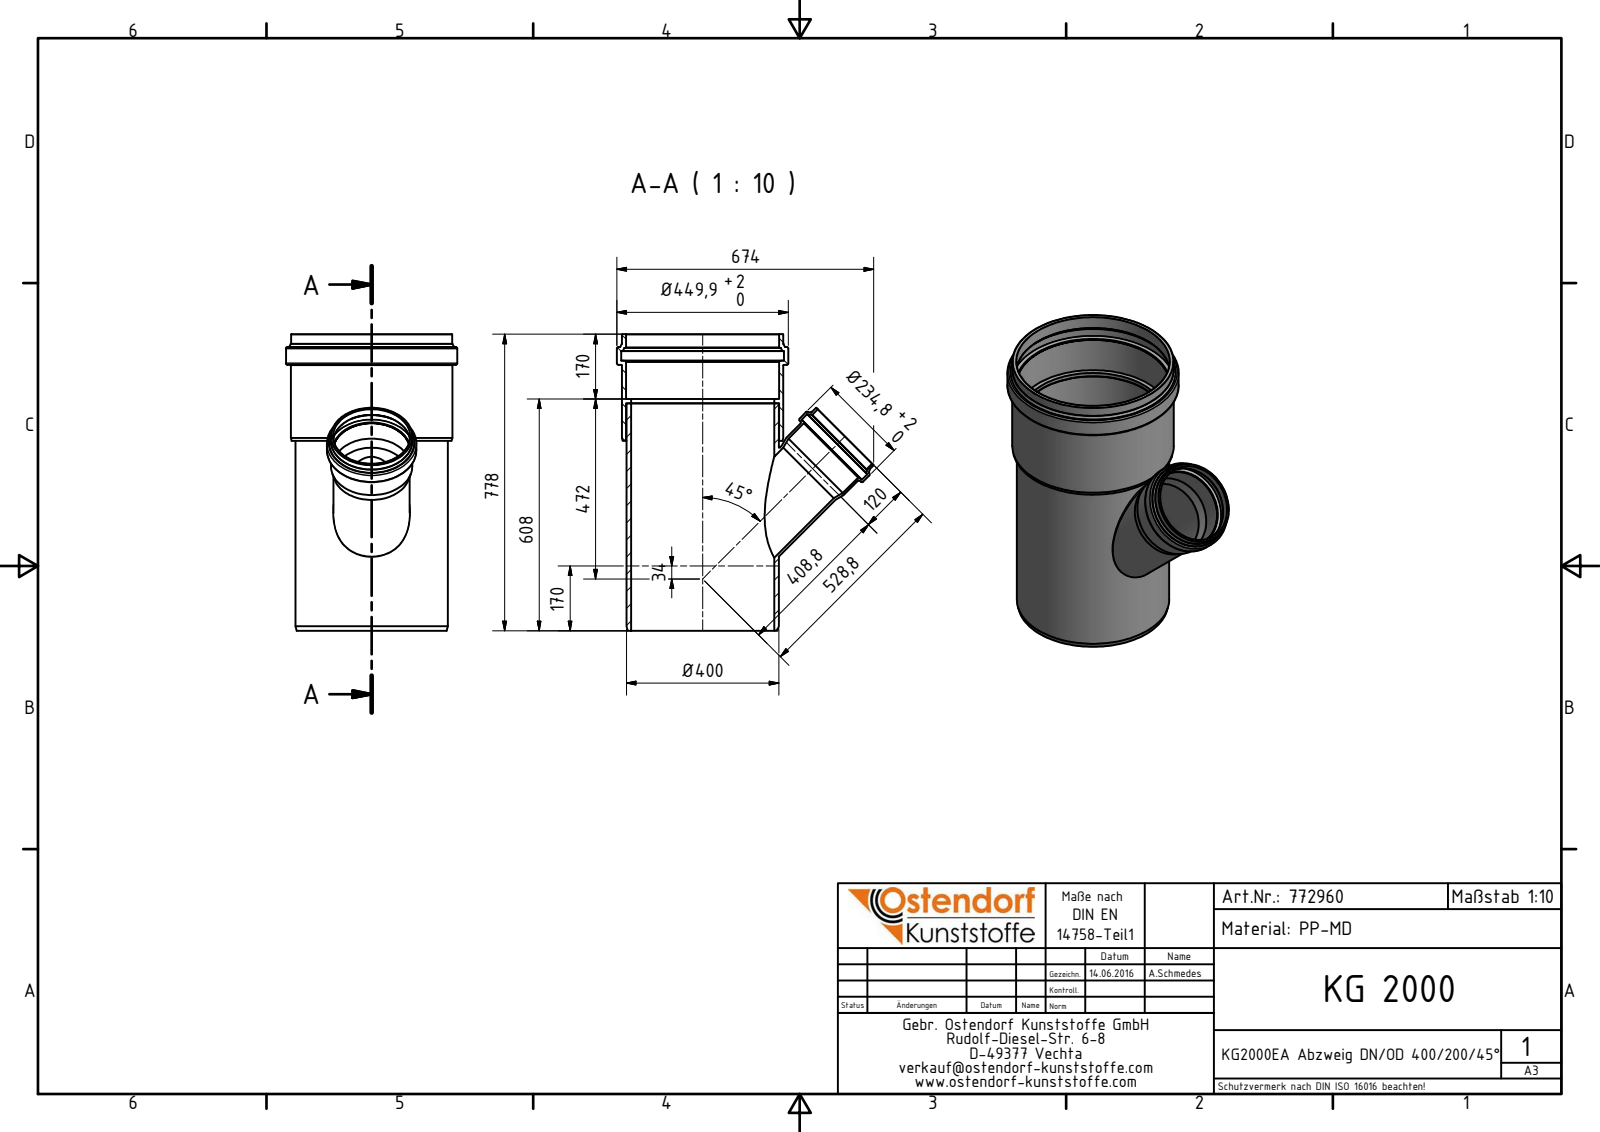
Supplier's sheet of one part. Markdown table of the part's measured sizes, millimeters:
| quantity | value |
| --- | --- |
| part name | 772960 KG2000EA Abzweig DN_OD 400_200 Teil 1; 772960 KG2000EA Abzweig DN_OD 400_200 Teil 2; 772960 KG2000EA Abzweig DN_OD 400_200 Zusammenbau |
| STEP written by | Autodesk Inventor 2016 (AUTOMOTIVE_DESIGN) |
| units | millimeters |
| bodies | 2 solids, 76 faces (13 planar, 20 cylindrical, 43 other) |
| overall size | 778 × 674 × 449.9 |
| volume | 13 860 000 mm³ |
| surface area | 2 601 000 mm² |
| round holes (diameter × count) | 201.8 × 2, 187.2 × 1, 201.5 × 1, 223 × 1, 376 × 1, 401.7 × 1, 402.1 × 1, 427.7 × 1 |
| round bosses / shafts (diameter × count) | 449.9 × 1, 423.9 × 1, 423.06 × 1, 400 × 1, 234.8 × 1, 213.6 × 1, 213.3 × 1, 200.2 × 1 |
| main face-to-face distances | 11.1, 98.9, 110, 280, 181.1, 170, 498, 596.9, 608, 778 |
